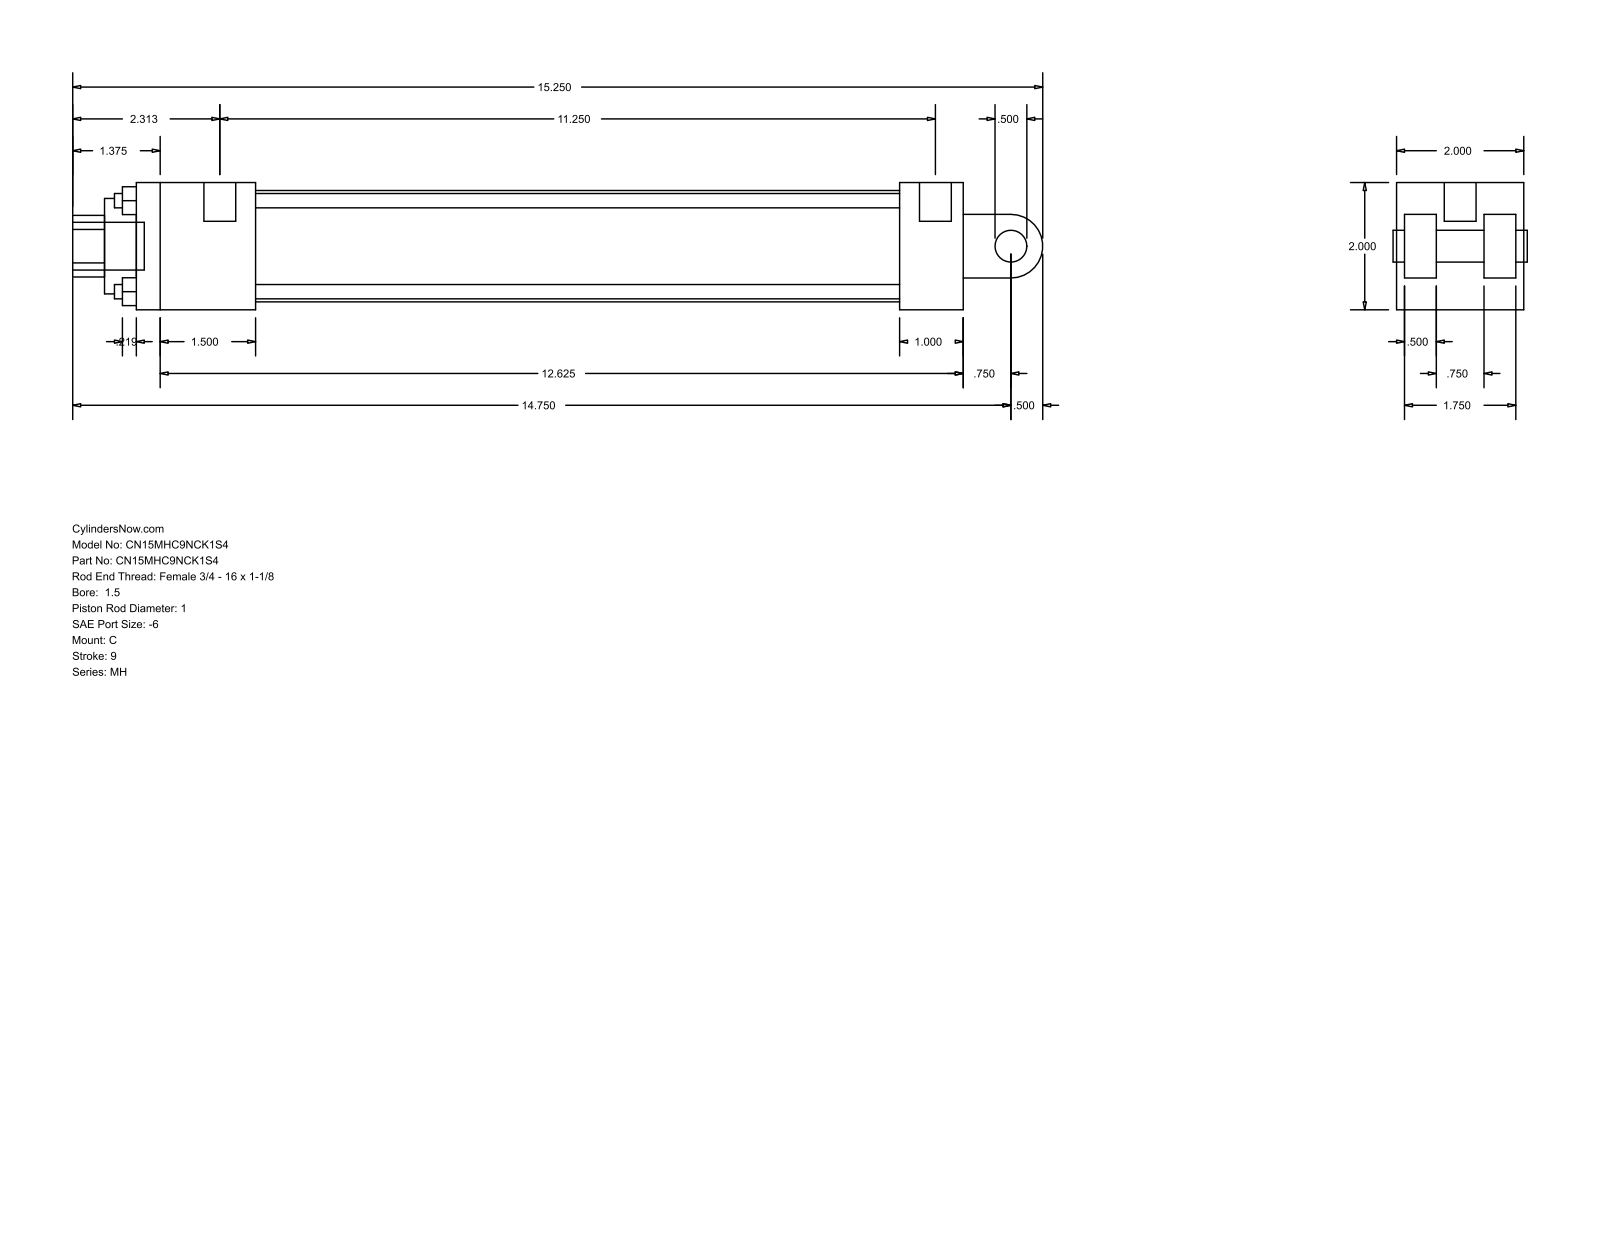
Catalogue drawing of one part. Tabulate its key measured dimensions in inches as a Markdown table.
| quantity | value |
| --- | --- |
| part name | MH_C__0150_1 |
| STEP written by | GSSL Pune (CONFIG_CONTROL_DESIGN) |
| units | inches |
| bodies | 0 solids, 99 faces (70 planar, 29 cylindrical, 0 other) |
| overall size | 15.25 × 2 × 2 |
| round holes (diameter × count) | 0.225 × 4, 0.219 × 2, 0.5 × 1, 1 × 1, 1.5 × 1, 1.75 × 1 |
| round bosses / shafts (diameter × count) | 0.5 × 2, 0.219 × 2, 0.75 × 1 |
| partial cylindrical surfaces (radius × count) | 0.484 × 1, 0.5 × 1 |
| main face-to-face distances | 2, 0.5, 1.875, 0.125, 0.625, 1, 1.375, 1.25, 13, 1.5 |
| hole center spacings | 1.011, 1.43, 2.022 |
